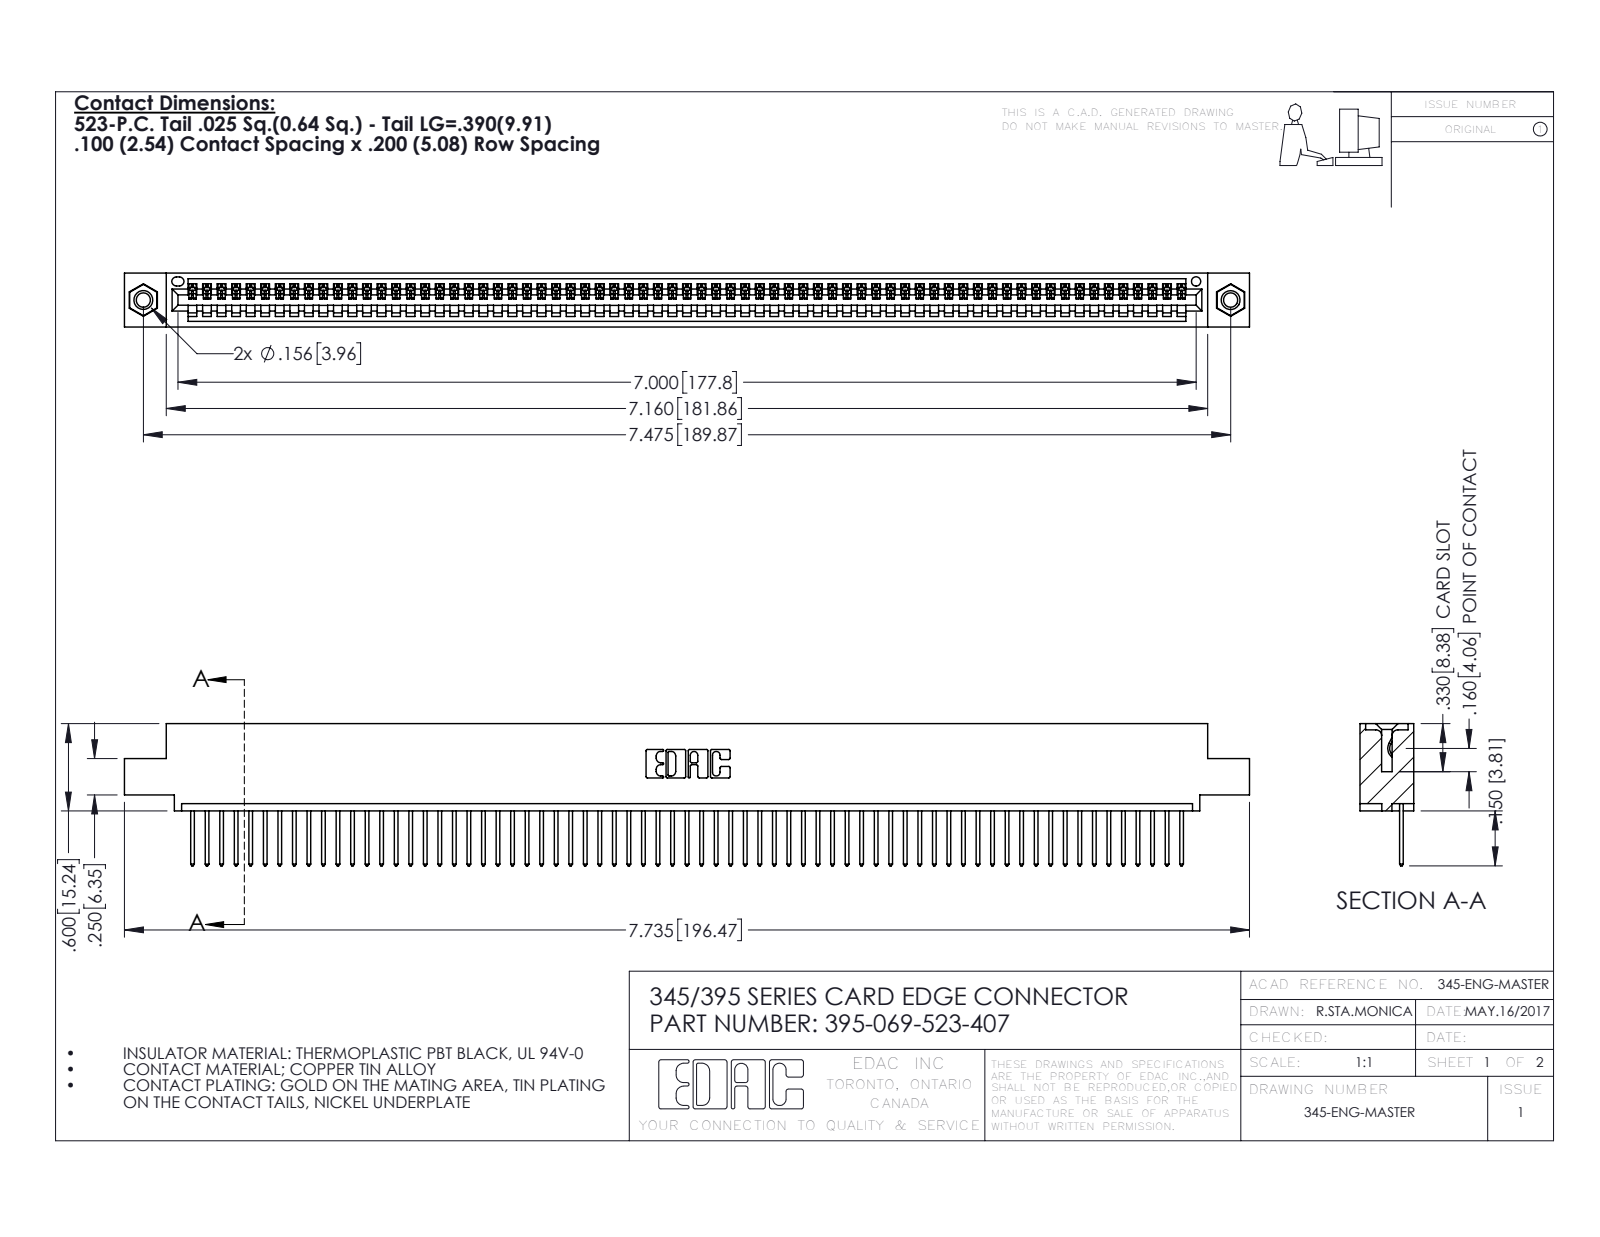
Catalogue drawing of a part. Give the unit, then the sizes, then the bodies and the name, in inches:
Units: inches
Overall size (bounding box): 7.735 × 0.977 × 0.37
Round holes (diameter × count): ⌀0.098 ×2, ⌀0.125 ×2, ⌀0.156 ×2, ⌀0.064 ×1
Round bosses / shafts (diameter × count): ⌀0.155 ×2
Partial cylindrical surfaces — rounded edges, fillets, slot ends (radius × count): R0.006 ×138, R0.01 ×138, R0.01 ×22, R0.007 ×6, R0.031 ×6, R0.026 ×3, R0.031 ×2, R0.04 ×2
Main face-to-face distances: 0.072, 0.298, 0.37, 0.2, 0.098, 0.272, 0.025, 0.225, 0.149, 0.072
Hole centre spacings: 0.27, 7.239, 7.475
Volume: 1.145 in³ · Surface area: 39.52 in²
Bodies: 72 solids, 4192 faces (2876 planar, 1300 cylindrical, 16 other)
Part name (STEP PRODUCT): 345 Part_0.110 Offset - 0.156 Dia-TI; 345-250-001_345-250-005-103; 395-069-523-407; 345-292-001_345-293-123
STEP written by: SolidWorks 2016 (CONFIG_CONTROL_DESIGN)
